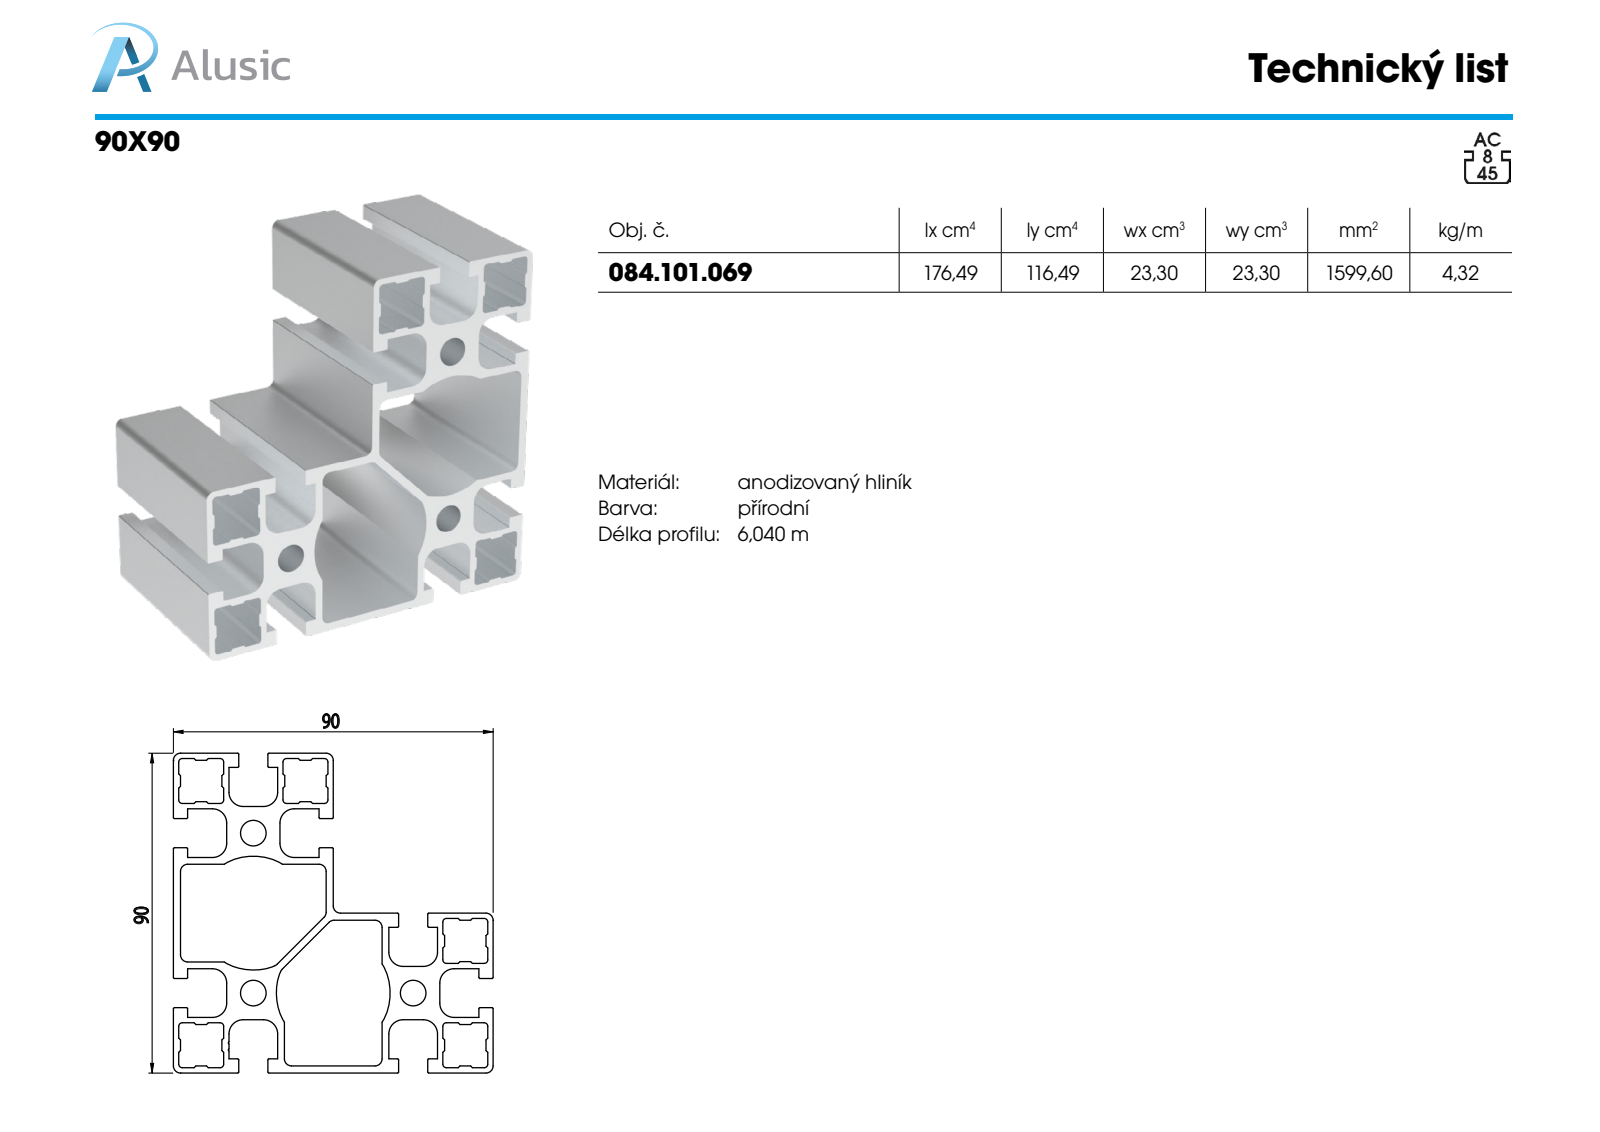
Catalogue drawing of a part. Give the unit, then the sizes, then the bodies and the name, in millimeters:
Units: millimetres
Overall size (bounding box): 100 × 90 × 90
Round holes (diameter × count): ⌀7.2 ×3
Partial cylindrical surfaces — rounded edges, fillets, slot ends (radius × count): R0.3 ×32, R1 ×20, R2 ×16, R4 ×16, R0.2 ×6, R16 ×2
Main face-to-face distances: 45, 2, 15.65, 29.35, 74.35, 1.5, 14.15, 43, 90, 31.25
Hole centre spacings: 45, 63.64
Volume: 159 961 mm³ · Surface area: 126 089 mm²
Bodies: 1 solid, 287 faces (186 planar, 101 cylindrical, 0 other)
Part name (STEP PRODUCT): 084.101.069
STEP written by: SolidWorks 2018 (AUTOMOTIVE_DESIGN)
